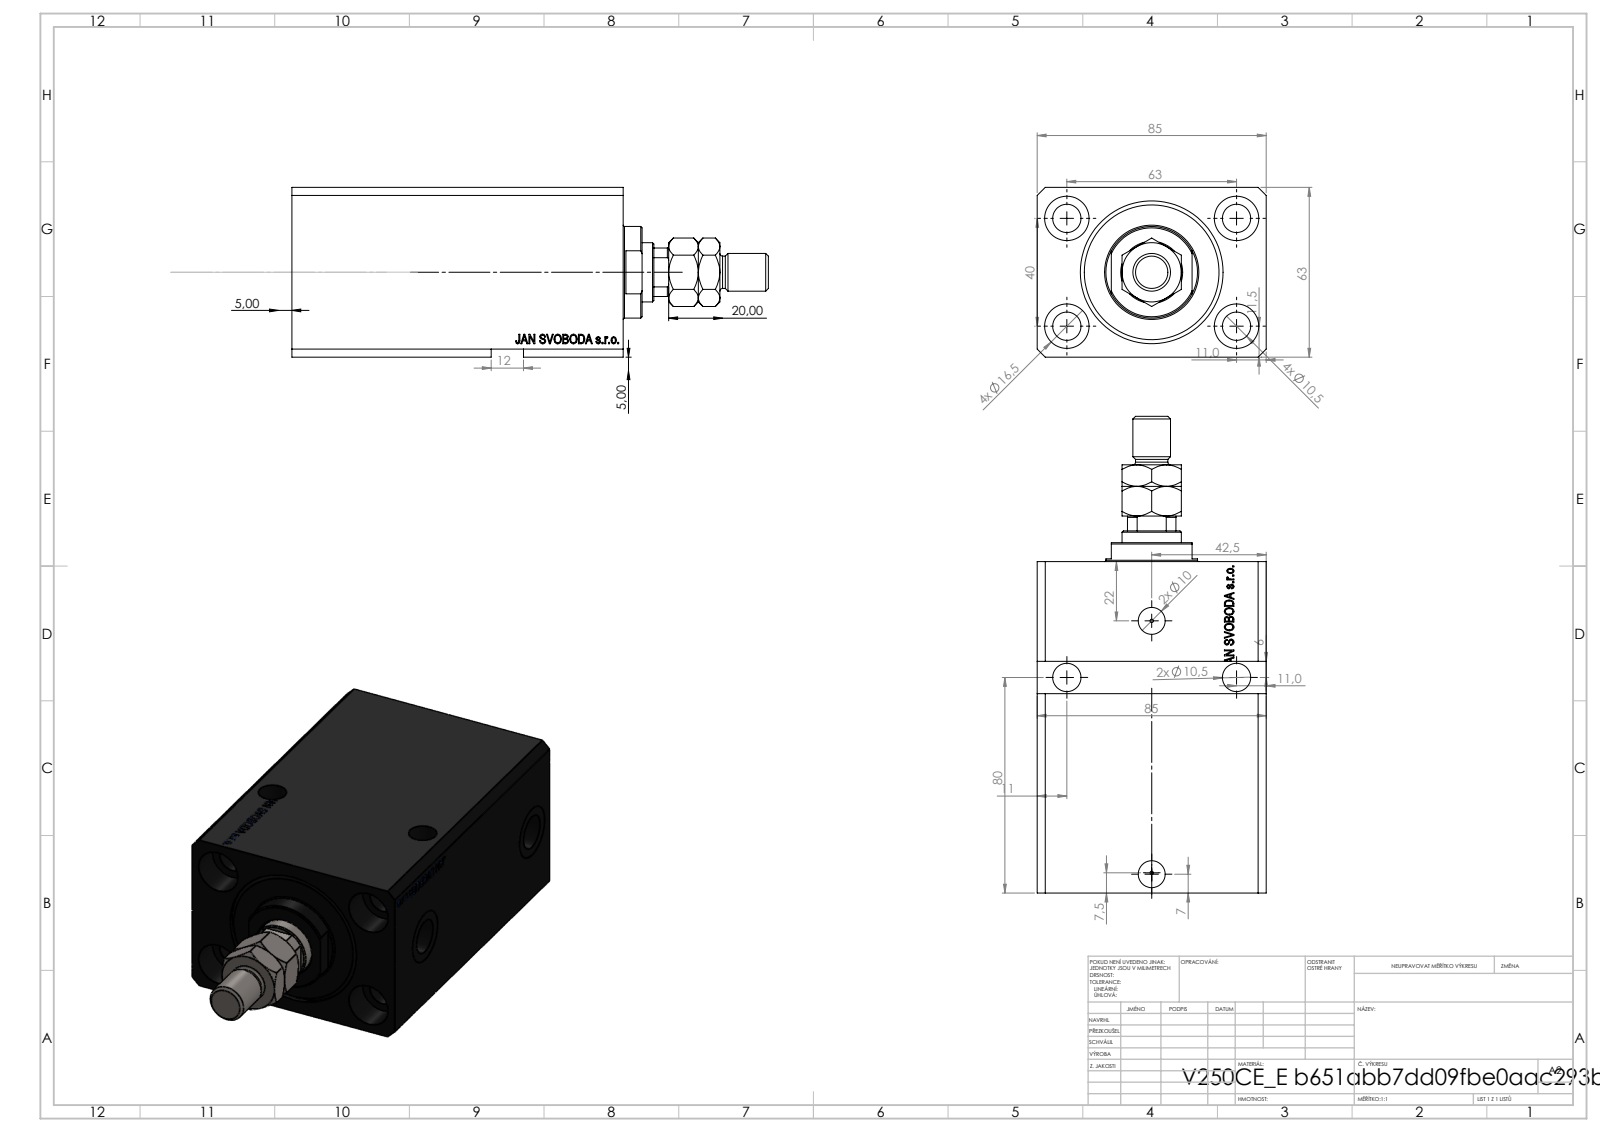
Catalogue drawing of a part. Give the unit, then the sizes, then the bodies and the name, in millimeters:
Units: millimetres
Overall size (bounding box): 177 × 85 × 63
Round holes (diameter × count): ⌀10.5 ×8, ⌀1.25 ×4, ⌀16.5 ×4, ⌀10 ×2, ⌀13.16 ×2, ⌀20 ×2, ⌀12.5 ×1, ⌀22 ×1, ⌀40 ×1, ⌀53 ×1
Round bosses / shafts (diameter × count): ⌀34 ×1, ⌀14 ×1, ⌀12 ×1
Partial cylindrical surfaces — rounded edges, fillets, slot ends (radius × count): R10.5 ×1
Main face-to-face distances: 63, 85, 17, 123, 106, 11.4, 94.6, 111.6, 56, 11
Hole centre spacings: 37.31, 63, 37.86, 40, 41.8, 42.15, 45, 73.13
Volume: 553 313 mm³ · Surface area: 110 806 mm²
Bodies: 4 solids, 986 faces (474 planar, 108 cylindrical, 404 other)
Part name (STEP PRODUCT): V250CE_E_Body; V250CE_VC_E; MTA; V250CE_C_VCP
STEP written by: SolidWorks 2019 (CONFIG_CONTROL_DESIGN)
